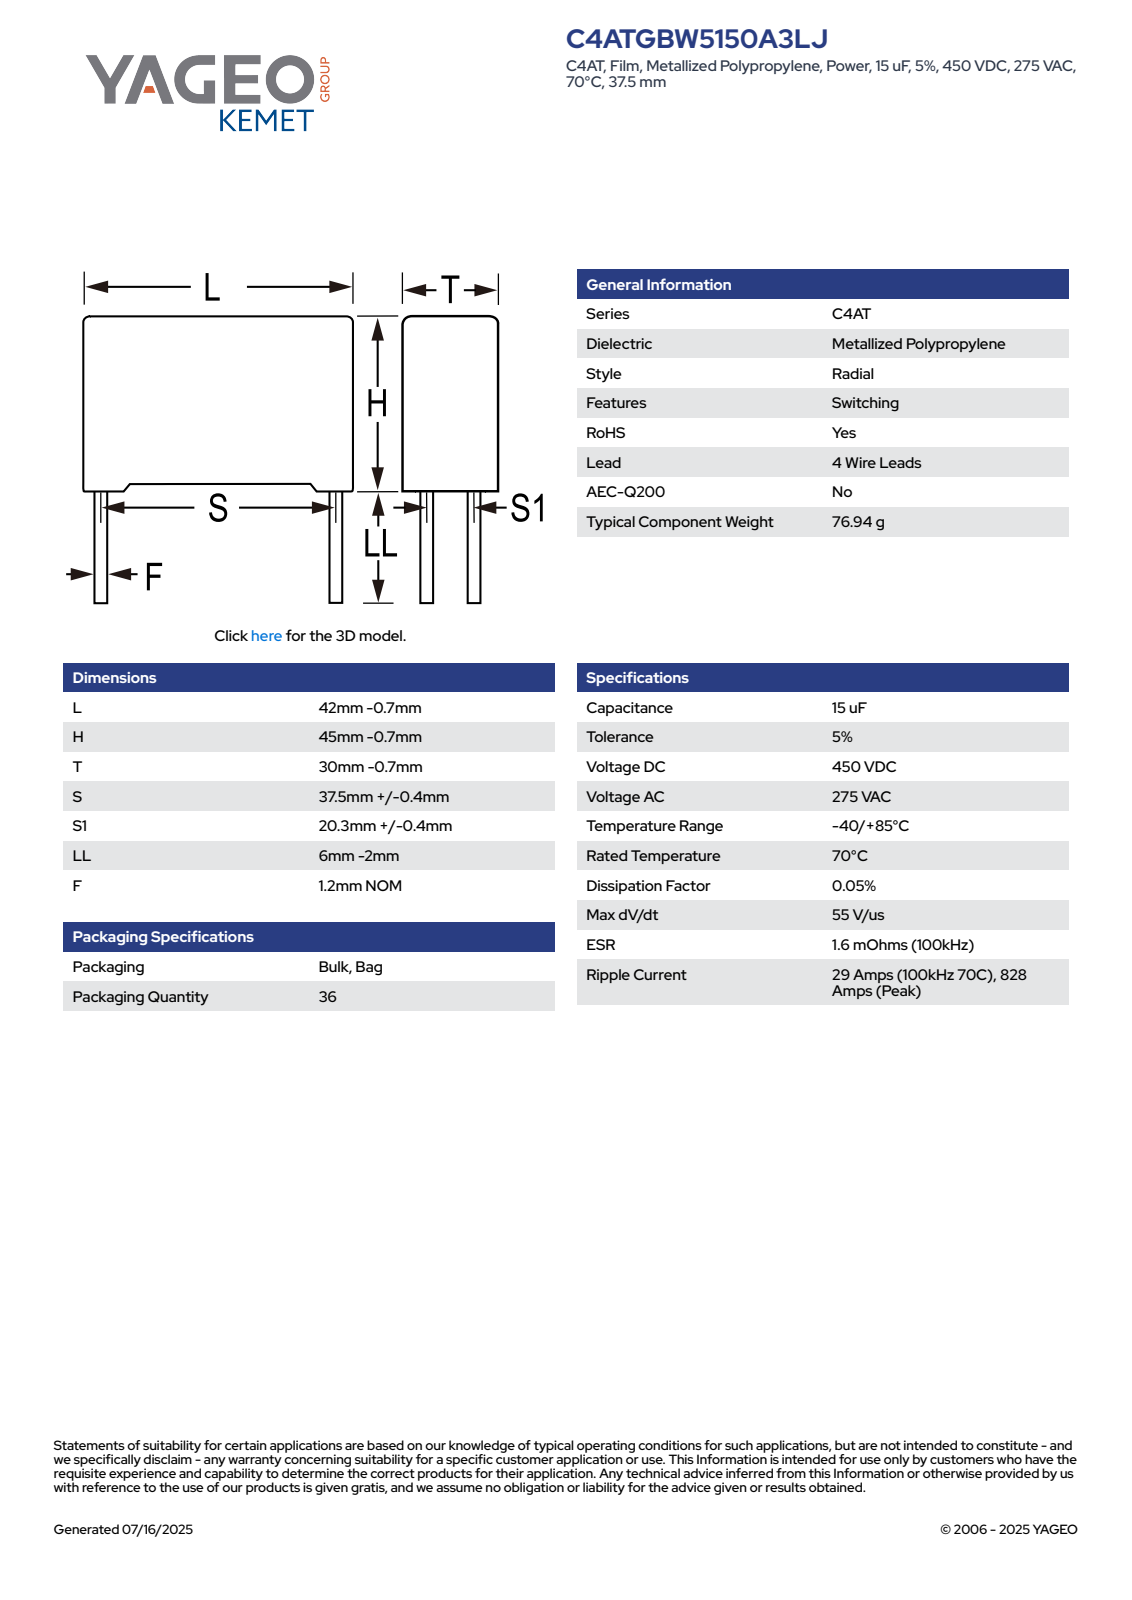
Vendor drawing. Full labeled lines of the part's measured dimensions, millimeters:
Part name (STEP PRODUCT): CFP_RB4_42X45X30_L41.3H44.3T29.3S37.5S120.3LL4F1.2
STEP written by: SolidWorks 2014 (AUTOMOTIVE_DESIGN)
Units: millimetres
Bodies: 4 solids, 91 faces (83 planar, 8 cylindrical, 0 other)
Overall size (bounding box): 48.3 × 41.3 × 29.3
Volume: 52 237 mm³ · Surface area: 8 876 mm²
Round bosses / shafts (diameter × count): ⌀1.2 ×4
Main face-to-face distances: 29.3, 41.3, 43, 1.3, 44.3, 1.8, 39.5, 37.7, 27.5, 25.7
